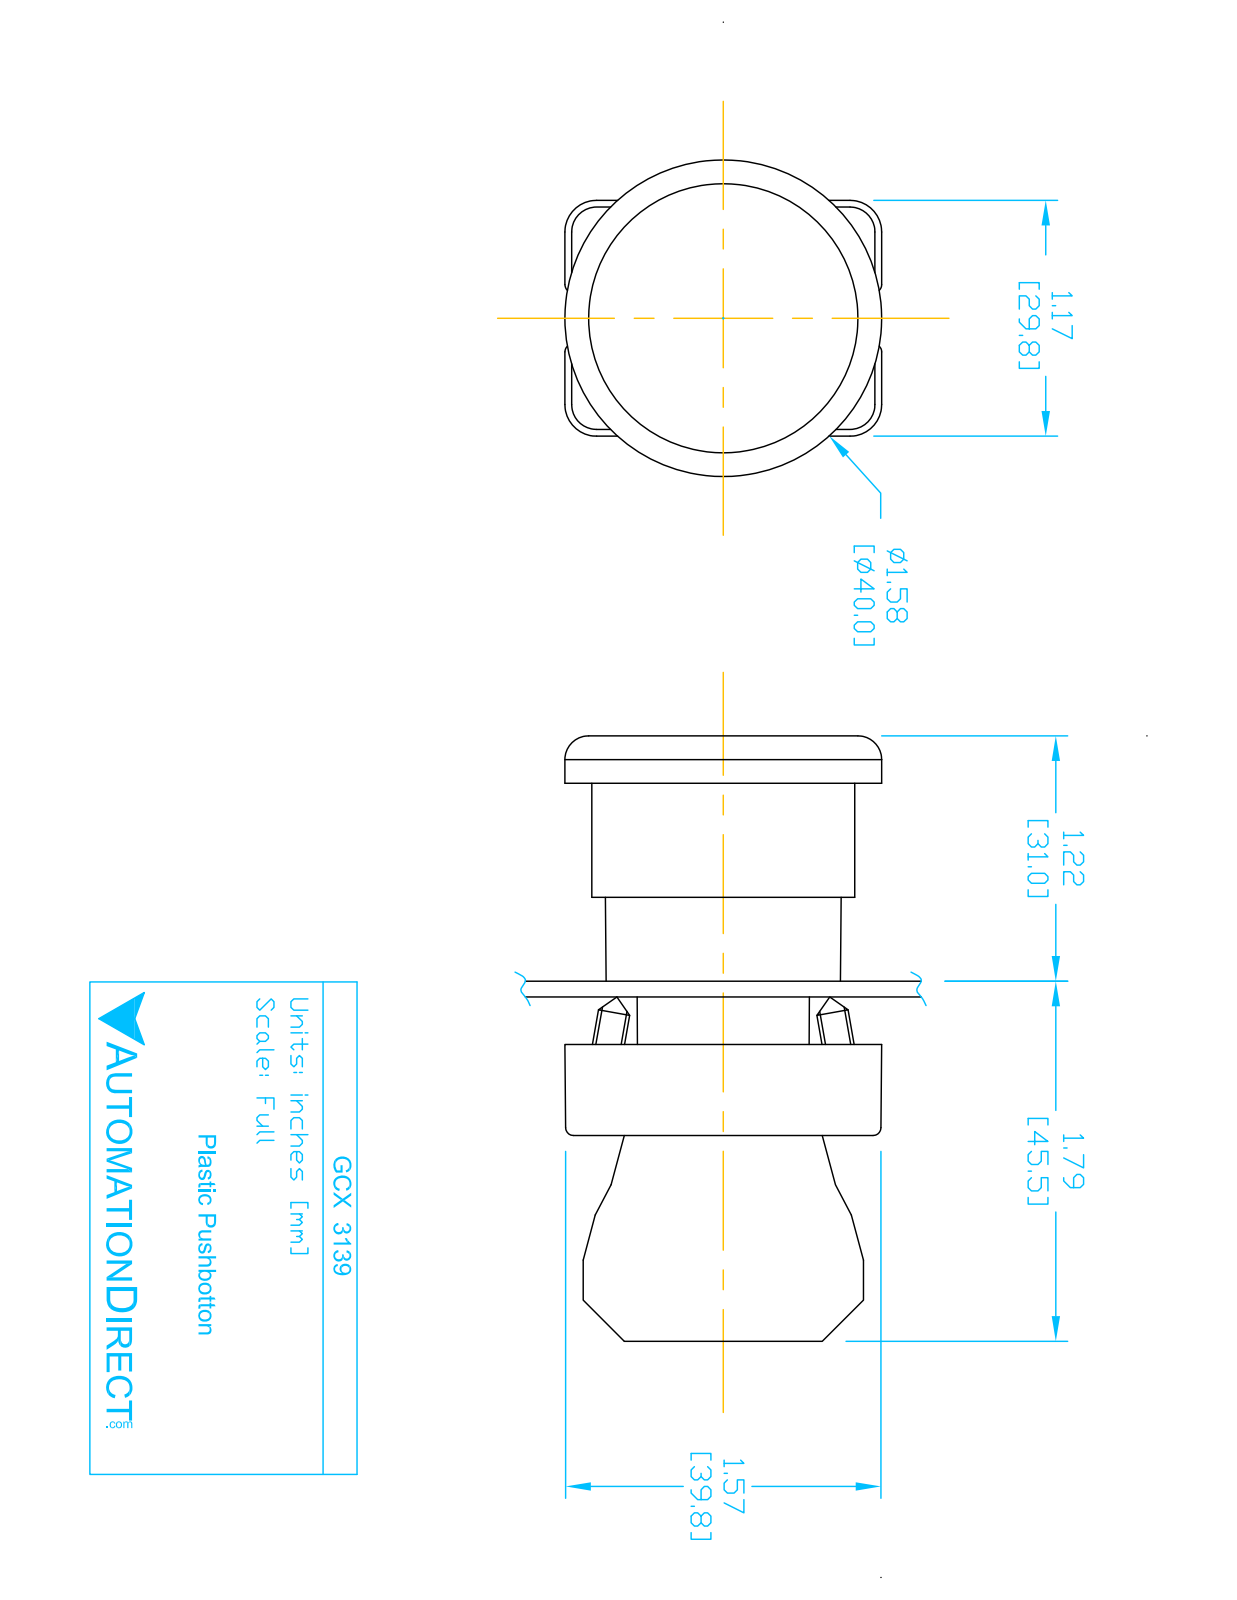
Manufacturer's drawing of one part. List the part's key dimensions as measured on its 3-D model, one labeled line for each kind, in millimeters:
Part name (STEP PRODUCT): ECX3029-2; ecx1040; GCX3139; GCX3139 OPERATOR
STEP written by: SolidWorks 2016 (AUTOMOTIVE_DESIGN)
Units: millimetres
Bodies: 6 solids, 389 faces (224 planar, 134 cylindrical, 31 other)
Overall size (bounding box): 74.8 × 40.2 × 40
Volume: 29 940 mm³ · Surface area: 21 550 mm²
Round holes (diameter × count): ⌀2 ×2, ⌀3.1 ×2, ⌀3.3 ×2, ⌀2.2 ×1, ⌀5 ×1, ⌀22.3 ×1, ⌀22.6 ×1, ⌀26 ×1, ⌀30 ×1
Round bosses / shafts (diameter × count): ⌀4 ×2, ⌀33 ×1, ⌀29.8 ×1, ⌀24 ×1, ⌀21.7 ×1, ⌀19.8 ×1
Partial cylindrical surfaces — rounded edges, fillets, slot ends (radius × count): R1.5 ×24, R1 ×12, R3.1 ×12, R4 ×12, R1 ×4, R3.3 ×2, R0.5 ×1, R1.6 ×1
Main face-to-face distances: 48.8, 14.7, 0.8, 44.8, 4, 0.8, 18.3, 26.5, 30.5, 17.5
Hole centre spacings: 6, 13.8, 12, 12.4
